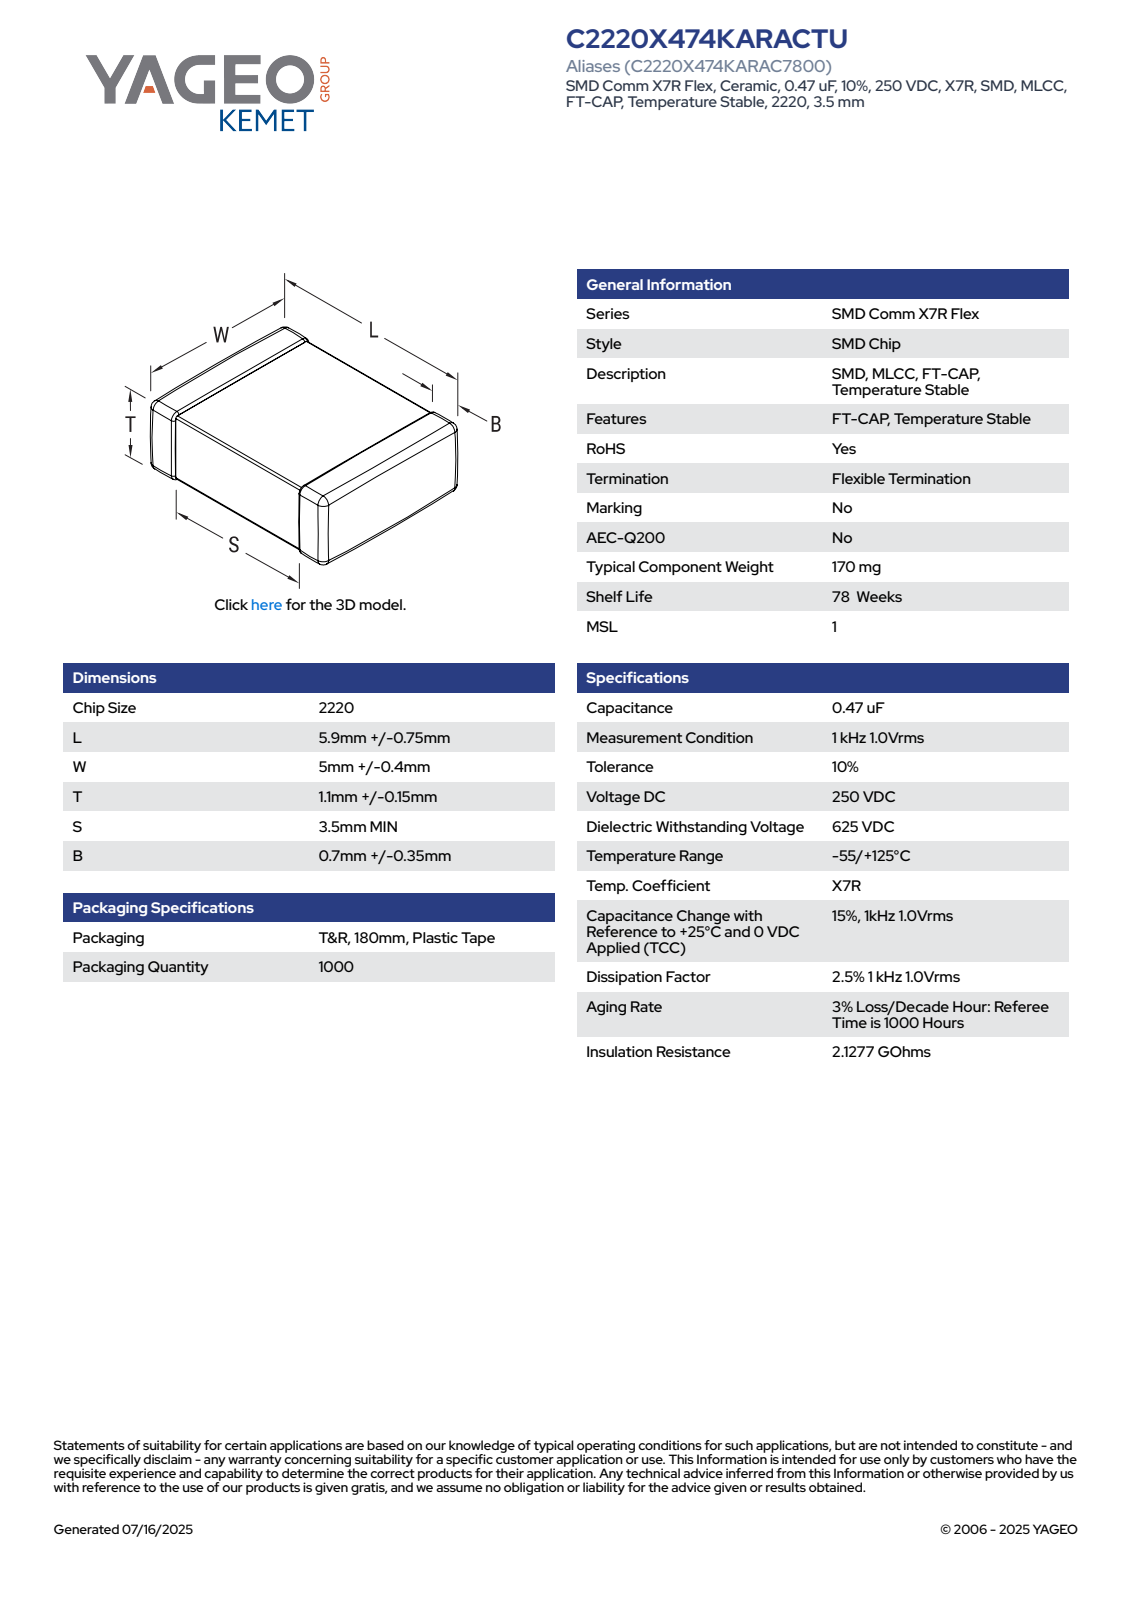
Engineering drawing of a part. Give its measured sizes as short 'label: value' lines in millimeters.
name: CCS_CCSTD_2220_L6.65W5.4T1.25B0.7
written by: SolidWorks 2021 (AUTOMOTIVE_DESIGN)
unit: mm
bodies: 4 solids, 121 faces (71 planar, 34 cylindrical, 16 other)
size: 6.65 × 5.4 × 1.25
volume: 38 mm³; area: 101 mm²
rounds: 24× R0.11
face distances: 1.03, 1.14, 1.25, 6.65, 5.18, 5.29, 5.4, 2.8, 3.85, 3.59
